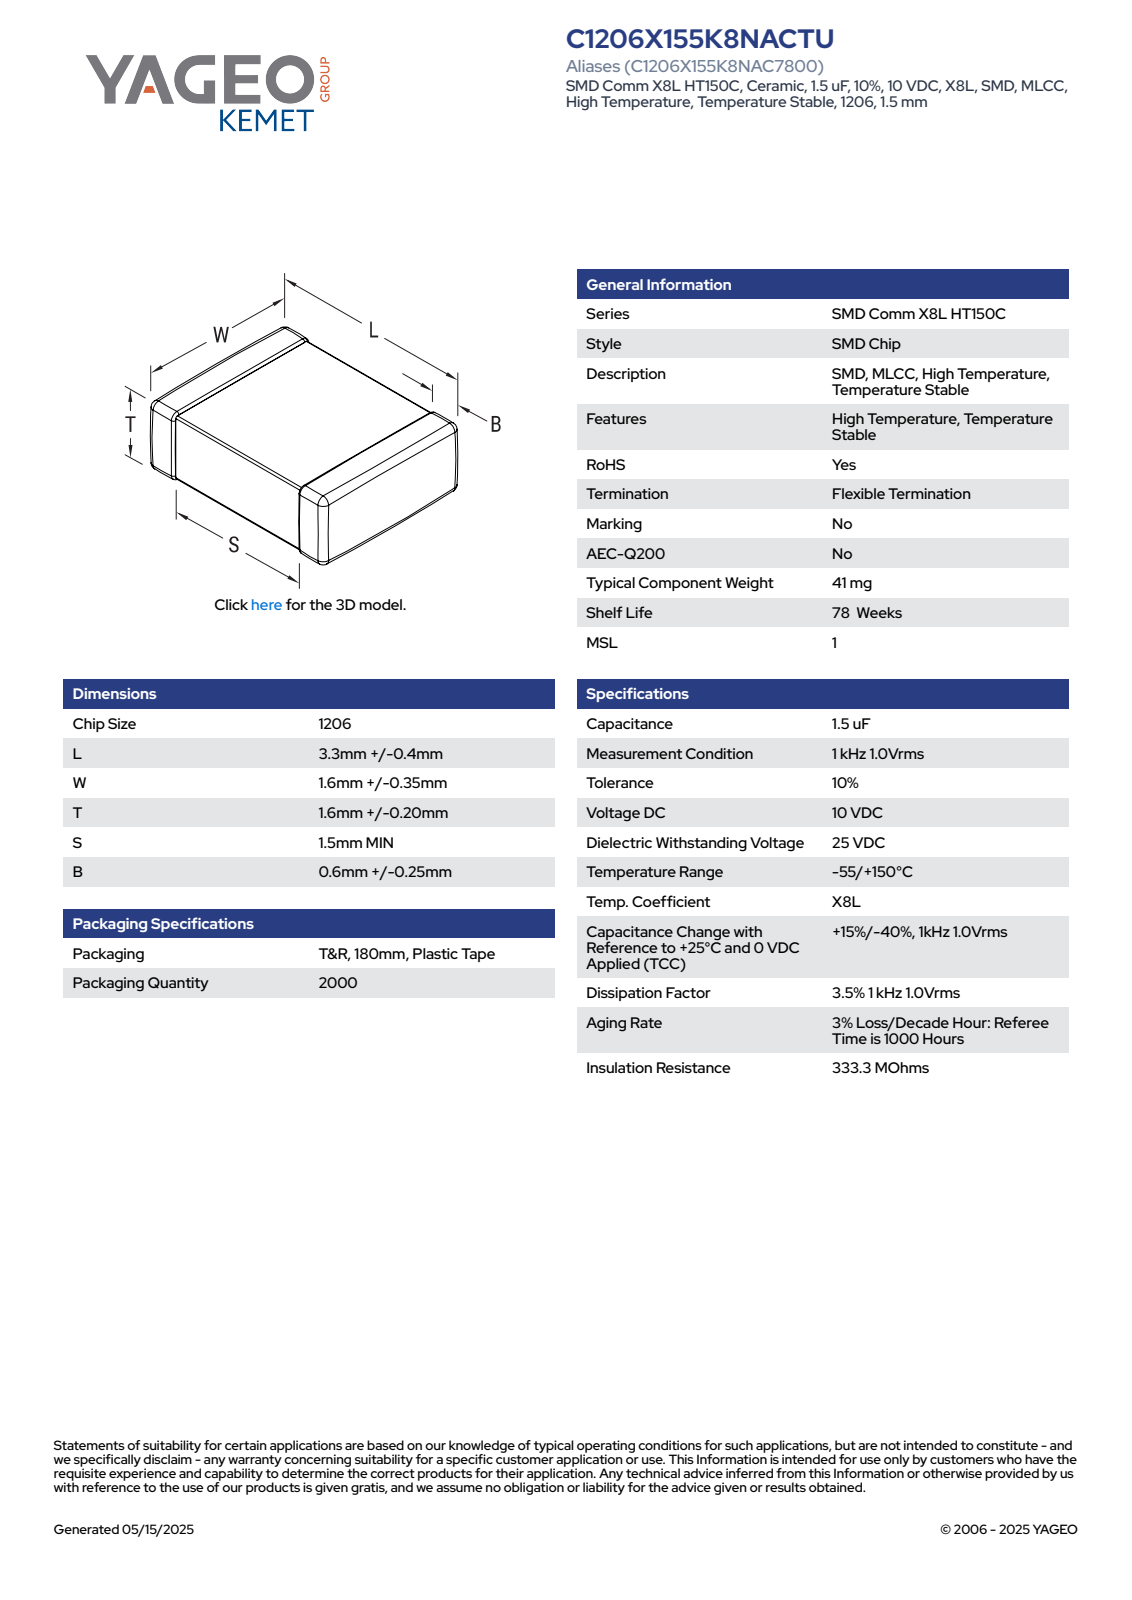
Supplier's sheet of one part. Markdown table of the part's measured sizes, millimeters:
| quantity | value |
| --- | --- |
| part name | CCS_CCSTD_1206_L3.7W1.95S1.6T1.8B0.6 |
| STEP written by | SolidWorks 2021 (AUTOMOTIVE_DESIGN) |
| units | millimeters |
| bodies | 4 solids, 125 faces (71 planar, 38 cylindrical, 16 other) |
| overall size | 3.7 × 1.95 × 1.8 |
| volume | 12 mm³ |
| surface area | 34 mm² |
| main face-to-face distances | 1.76, 1.91, 1.72, 1.87, 3.7, 1.8, 1.95, 1.71, 1.99, 2 |
